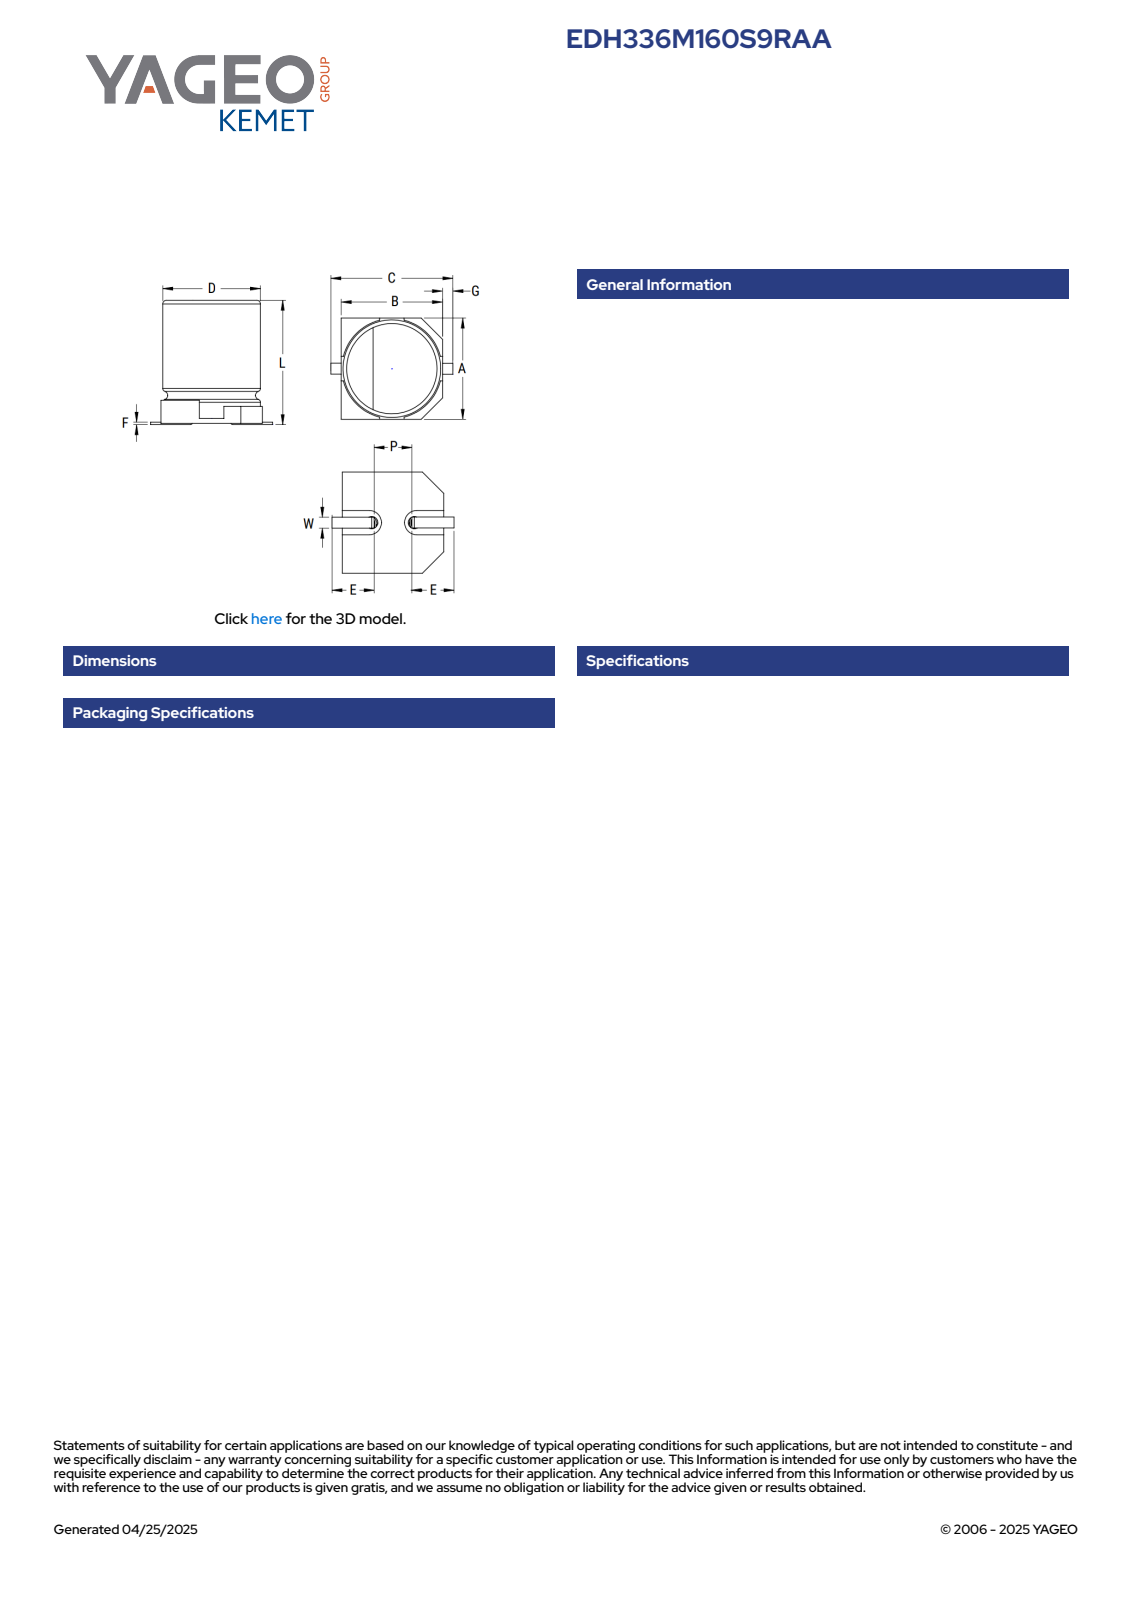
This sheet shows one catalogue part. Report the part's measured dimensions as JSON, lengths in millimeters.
{"part_name": "CAC_S_12.5X13.5_D13L14W1.45F0.3A13B13C15.2E5.1P4.8", "step_written_by": "SolidWorks 2014 (AUTOMOTIVE_DESIGN)", "units": "millimeters", "bodies": {"solids": 5, "faces": 78, "planar": 61, "cylindrical": 11, "other": 6}, "overall_size": [15, 14.01, 13], "volume_mm3": 1734, "surface_area_mm2": 1276, "round_bosses_or_shafts": [[12.43, 1]], "partial_cylinders_radius": [[0.2, 2], [5.16, 1], [6.5, 1]], "face_to_face_distances": [0.7, 13, 13.7, 3.5, 2.8, 10.2, 1, 14, 3.8, 2.63]}
